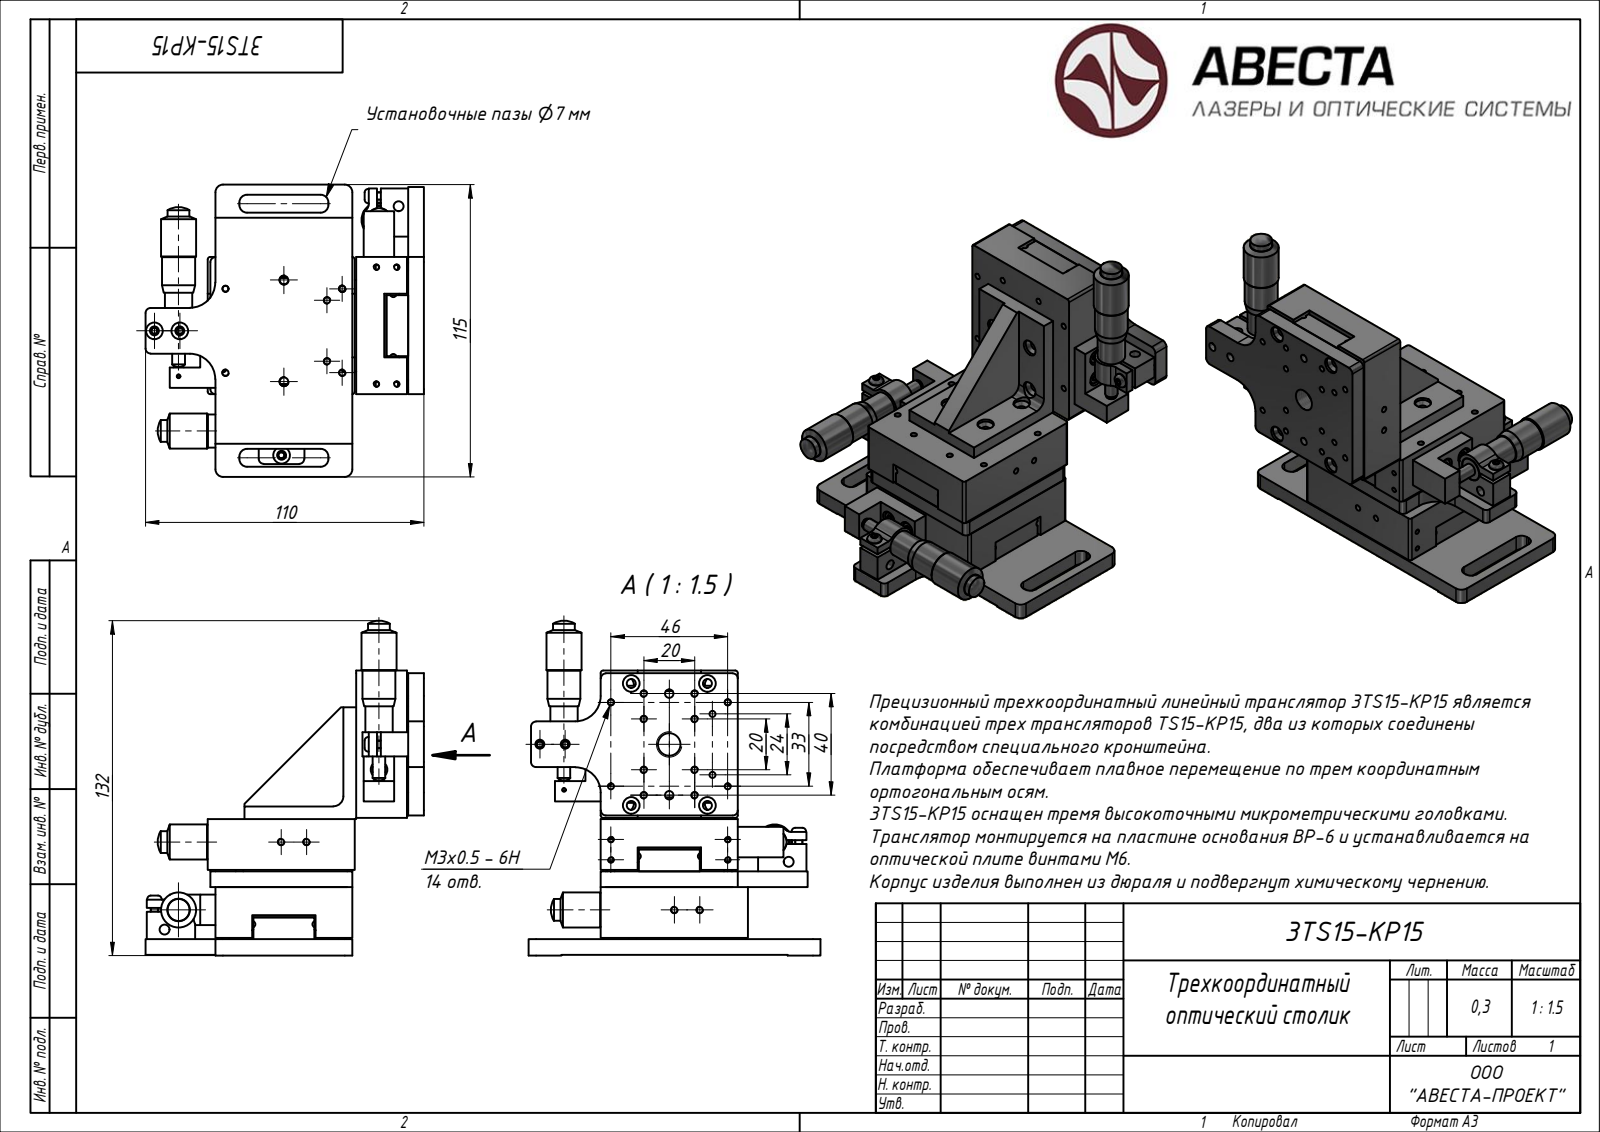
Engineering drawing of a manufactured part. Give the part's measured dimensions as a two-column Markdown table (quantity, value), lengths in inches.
| quantity | value |
| --- | --- |
| part name | Block 01 |
| STEP written by | ST-DEVELOPER v15 (AUTOMOTIVE_DESIGN) |
| units | inches |
| bodies | 22 solids, 1960 faces (0 planar, 0 cylindrical, 1960 other) |
| overall size | 5.189 × 4.528 × 4.317 |
